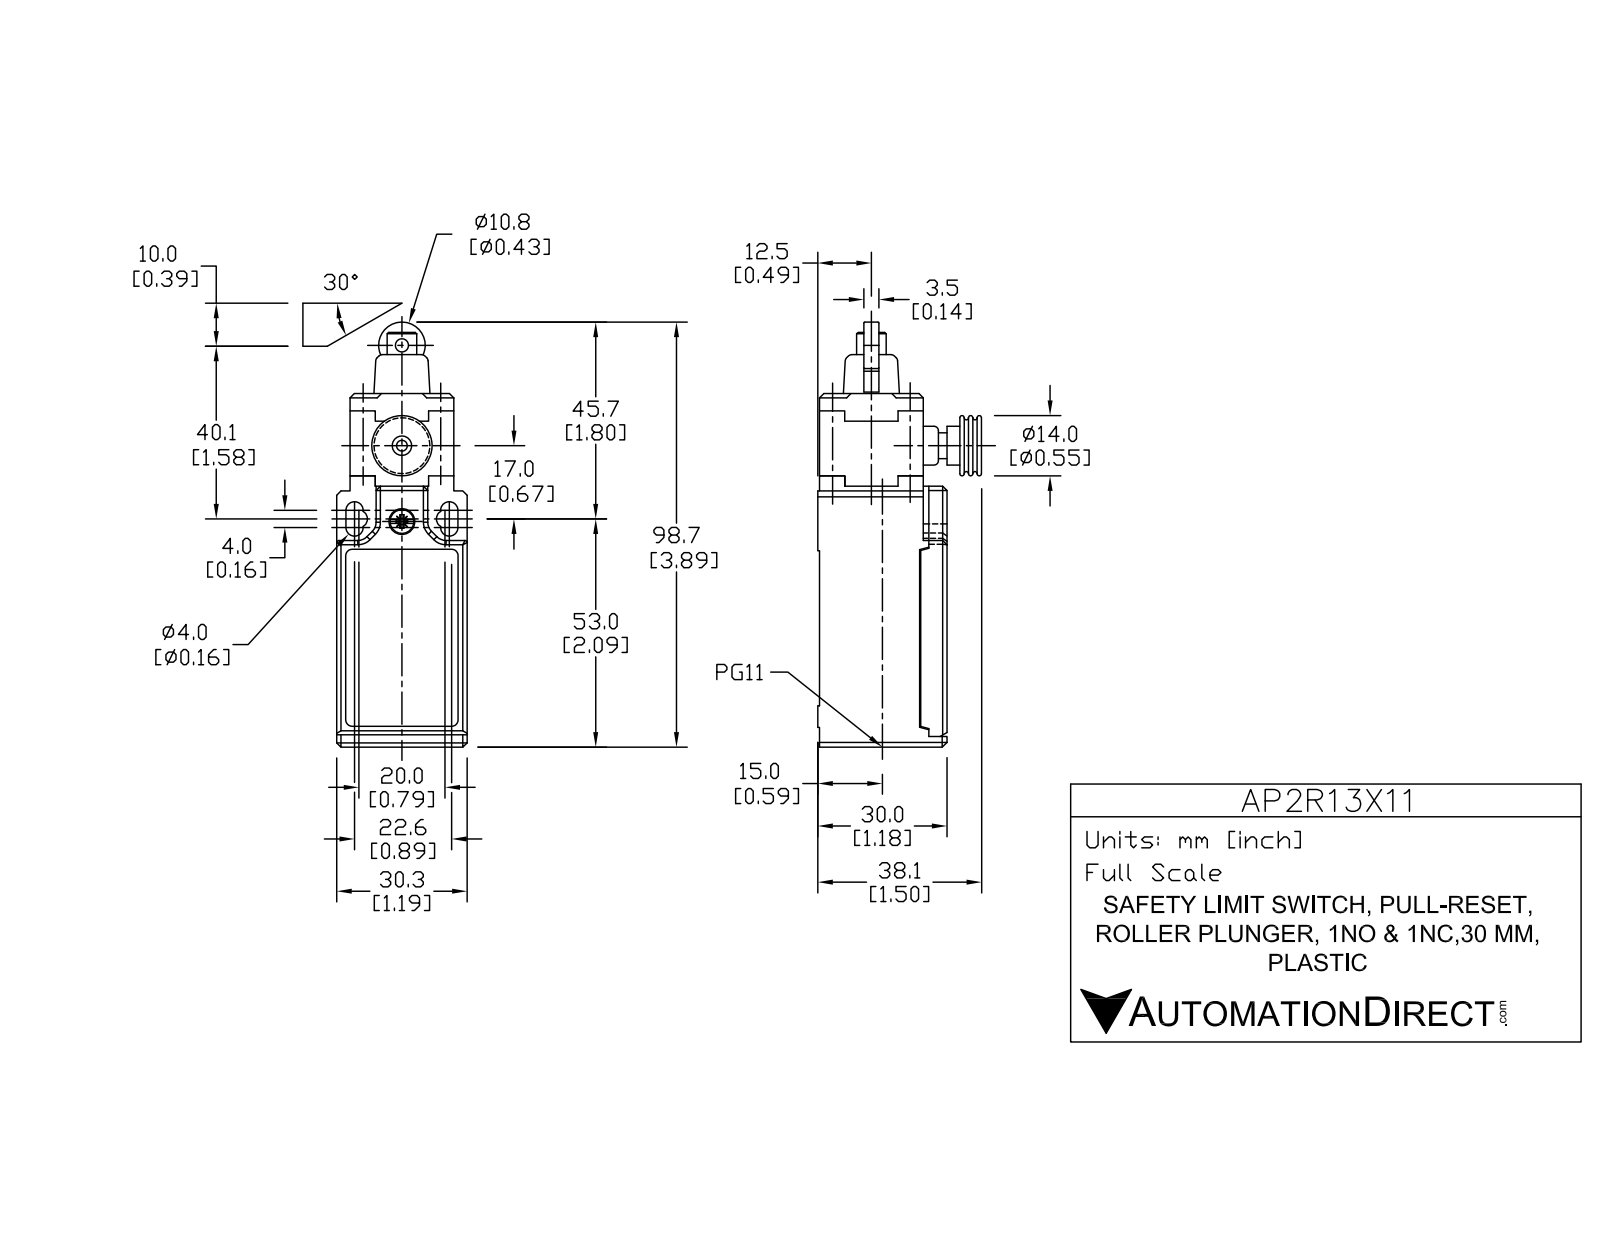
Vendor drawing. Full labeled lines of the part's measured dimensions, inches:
Part name (STEP PRODUCT): AP2R13X11
STEP written by: SolidWorks 2017 (AUTOMOTIVE_DESIGN)
Units: inches
Bodies: 5 solids, 267 faces (132 planar, 86 cylindrical, 49 other)
Overall size (bounding box): 3.925 × 1.474 × 1.193
Volume: 4.013 in³ · Surface area: 27.49 in²
Round holes (diameter × count): ⌀0.319 ×1, ⌀0.669 ×1, ⌀0.748 ×1
Round bosses / shafts (diameter × count): ⌀0.22 ×5, ⌀0.217 ×3, ⌀0.425 ×1, ⌀0.386 ×1, ⌀0.354 ×1, ⌀0.315 ×1, ⌀0.236 ×1, ⌀0.098 ×1
Partial cylindrical surfaces — rounded edges, fillets, slot ends (radius × count): R0.039 ×10, R0.118 ×8, R0.079 ×6, R0.02 ×4, R0.394 ×1, R0.4 ×1, R0.787 ×1
Main face-to-face distances: 1.193, 1.165, 0.945, 0.124, 1.069, 0.236, 0.594, 0.22, 0.094, 0.591
Hole centre spacings: 0.083
